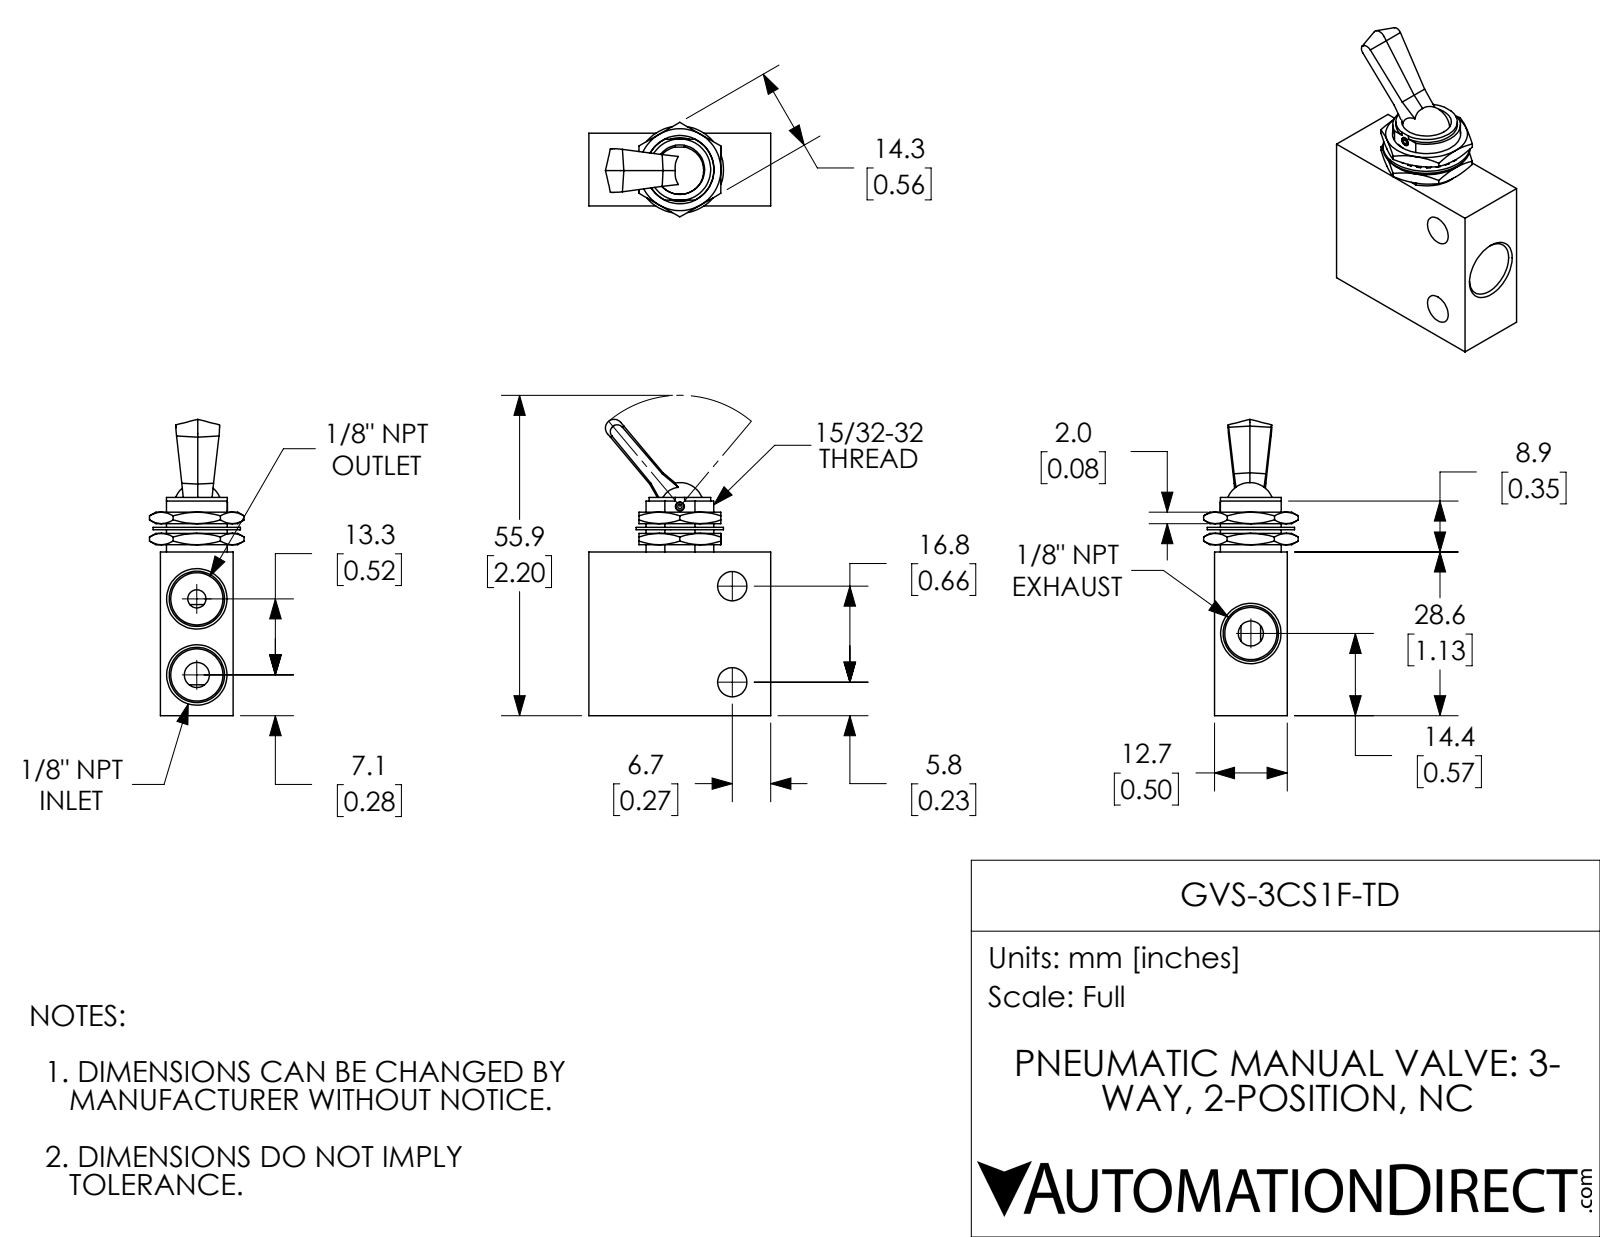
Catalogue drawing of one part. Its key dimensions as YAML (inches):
part_name: "GVS-3CS1F-TD"
step_written_by: "SolidWorks 2018 (AUTOMOTIVE_DESIGN)"
units: inches
bodies: {solids: 6, faces: 250, planar: 99, cylindrical: 87, other: 64}
overall_size: [2.037, 1.25, 0.65]
volume: 0.568
surface_area: 10.85
round_holes:
  - {diameter: 0.172, count: 2}
  - {diameter: 0.201, count: 2}
  - {diameter: 0.03, count: 1}
  - {diameter: 0.063, count: 1}
  - {diameter: 0.07, count: 1}
  - {diameter: 0.125, count: 1}
  - {diameter: 0.18, count: 1}
  - {diameter: 0.25, count: 1}
  - {diameter: 0.339, count: 1}
  - {diameter: 0.34, count: 1}
  - {diameter: 0.438, count: 1}
round_bosses_or_shafts:
  - {diameter: 0.6, count: 1}
  - {diameter: 0.423, count: 1}
  - {diameter: 0.063, count: 1}
partial_cylinders:
  - {radius: 0.233, count: 1}
  - {radius: 0.239, count: 1}
  - {radius: 0.26, count: 1}
face_to_face_distances: [0.5, 1.125, 1.25, 0.38, 0.87, 0.12, 0.145, 0.078, 0.041, 0.459]
hole_center_spacings: [0.238, 0.285, 0.523, 0.656, 0.66, 1.26]
